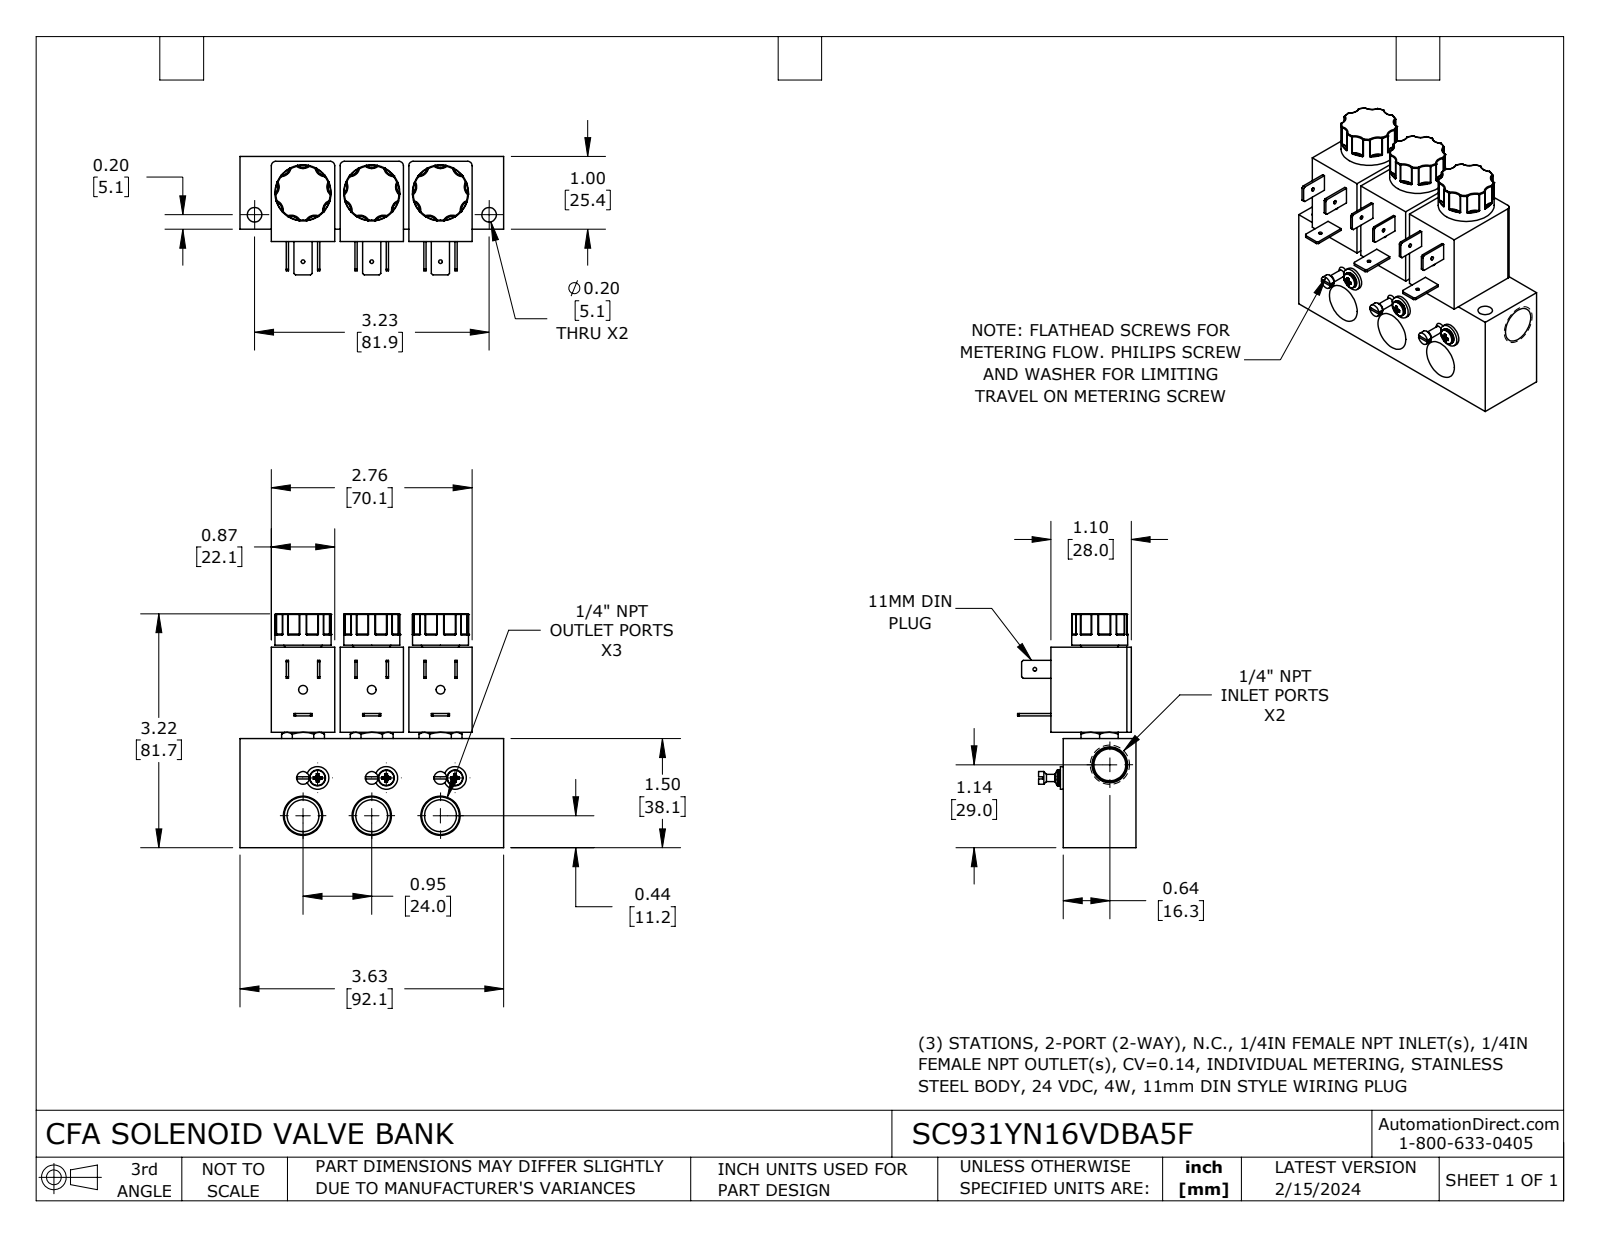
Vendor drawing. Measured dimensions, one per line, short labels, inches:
name: SC931YN16VDBA5F
written by: SolidWorks 2023 (CONFIG_CONTROL_DESIGN)
unit: in
bodies: 1 solid, 829 faces (215 planar, 197 cylindrical, 417 other)
size: 3.625 × 3.215 × 1.627
volume: 8.838 in³; area: 53.67 in²
holes: 4× ⌀0.05, 4× ⌀0.438, 3× ⌀0.12, 2× ⌀0.2
bosses: 3× ⌀0.77, 3× ⌀0.312, 3× ⌀0.219, 3× ⌀0.175, 3× ⌀0.1
rounds: 54× R0.01, 27× R0.133, 6× R0.06
face distances: 1, 0.945, 1.169, 0.169, 1.5, 0.945, 1.89, 0.065, 0.935, 1.104
hole spacings: 0.945, 0.945, 1.732, 1.89, 1.973, 1.973, 2.564, 0.928
